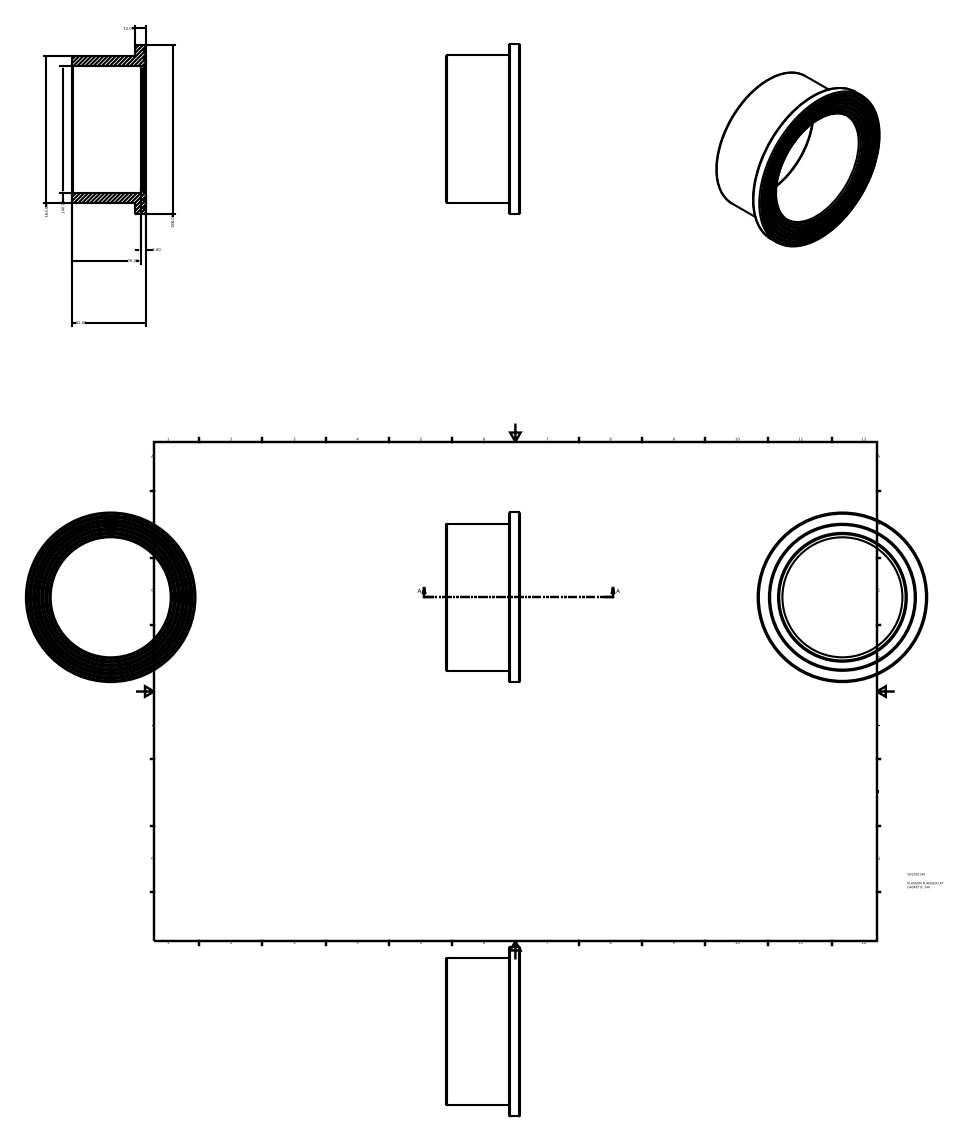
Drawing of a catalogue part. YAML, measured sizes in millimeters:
part_name: "055200140"
step_written_by: "Autodesk Inventor 2015 (AUTOMOTIVE_DESIGN)"
units: millimeters
bodies: {solids: 1, faces: 28, planar: 9, cylindrical: 4, other: 15}
overall_size: [188, 188, 82]
volume: 526971
surface_area: 106227
round_holes:
  - {diameter: 133, count: 1}
  - {diameter: 140, count: 1}
round_bosses_or_shafts:
  - {diameter: 188, count: 1}
  - {diameter: 163, count: 1}
face_to_face_distances: [70, 6, 82, 12, 80.2, 10.2, 1.8, 76, 4.2]
